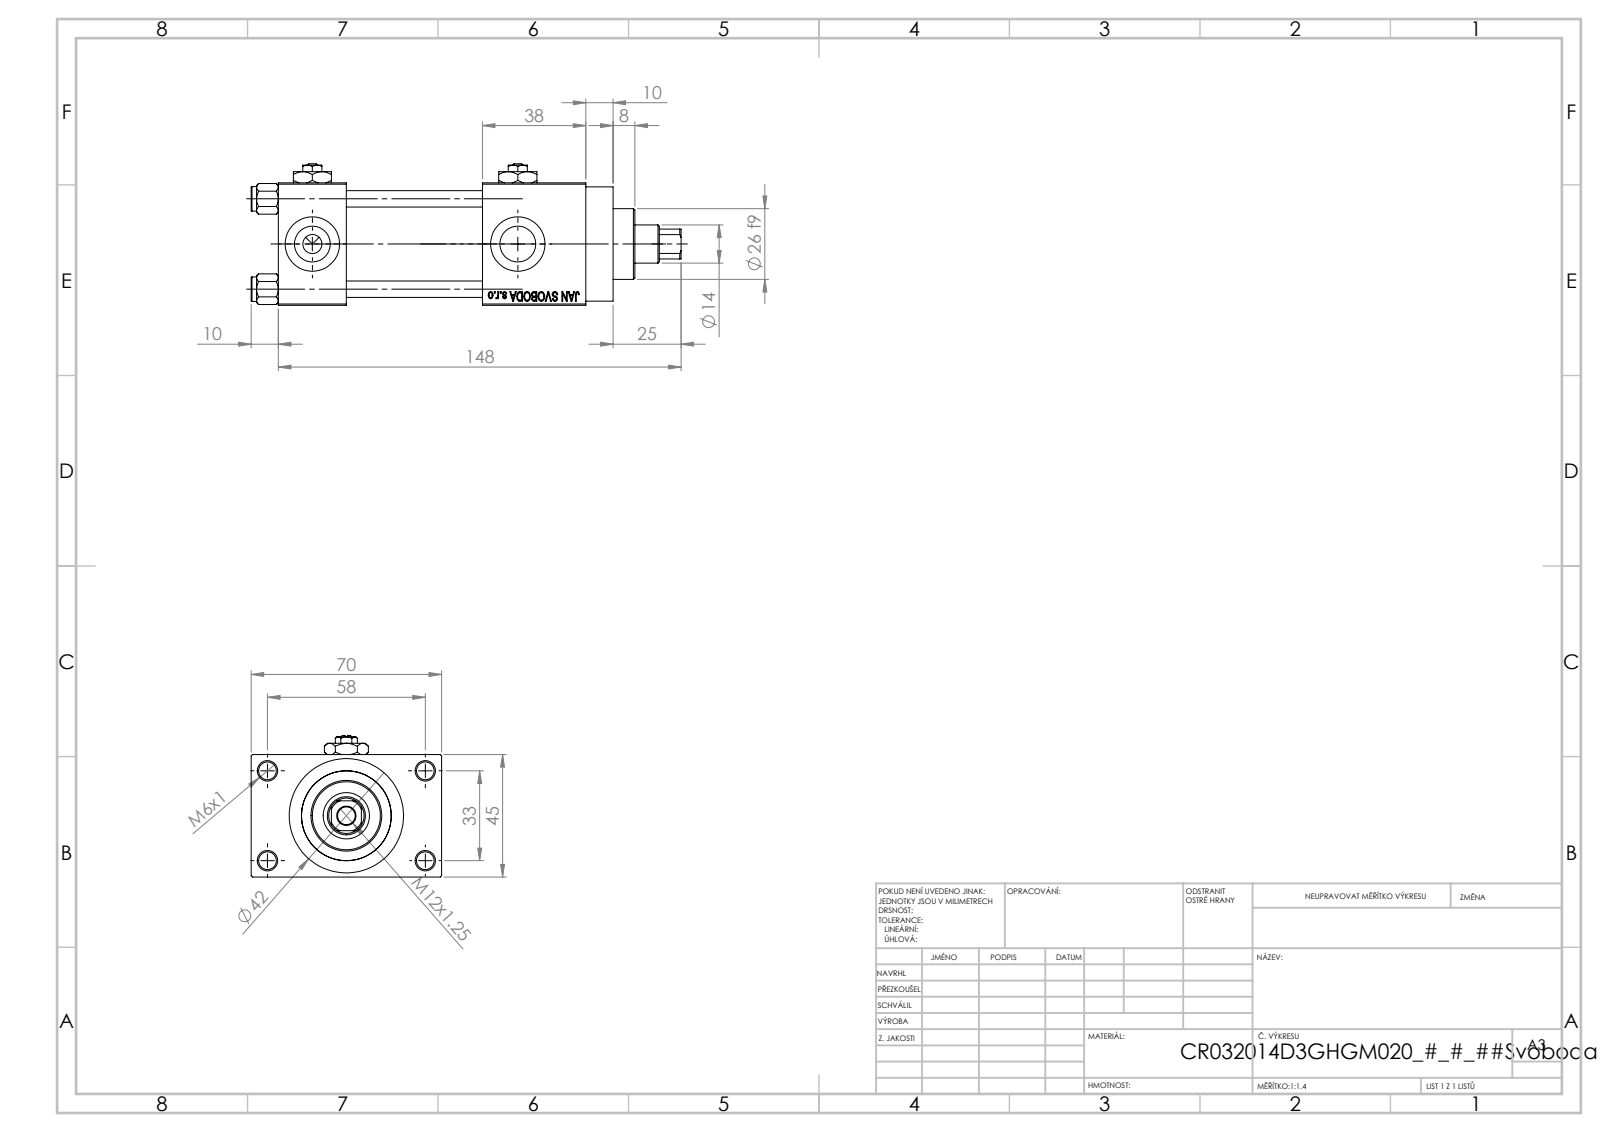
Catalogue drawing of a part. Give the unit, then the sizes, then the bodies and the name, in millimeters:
Units: millimetres
Overall size (bounding box): 158 × 70 × 52
Round holes (diameter × count): ⌀6.5 ×5, ⌀6 ×4, ⌀13.16 ×4, ⌀20 ×4, ⌀7 ×3, ⌀14 ×1, ⌀17 ×1, ⌀24 ×1, ⌀32 ×1, ⌀33 ×1
Round bosses / shafts (diameter × count): ⌀9 ×4, ⌀42 ×1, ⌀38 ×1, ⌀26 ×1
Partial cylindrical surfaces — rounded edges, fillets, slot ends (radius × count): R6.5 ×1
Main face-to-face distances: 45, 25, 50, 12.5, 75, 57.5, 88, 38, 113, 70
Hole centre spacings: 12.4, 23.48, 33.2, 33.37, 35.35, 45.6, 56.35, 33
Volume: 229 076 mm³ · Surface area: 77 129 mm²
Bodies: 13 solids, 1201 faces (542 planar, 99 cylindrical, 560 other)
Part name (STEP PRODUCT): Zatka_pro_OIL_PORT; V215CR_D_TYCINKA; V215CR_VCP_D; V215_VC_A (+2 more)
STEP written by: SolidWorks 2019 (CONFIG_CONTROL_DESIGN)
